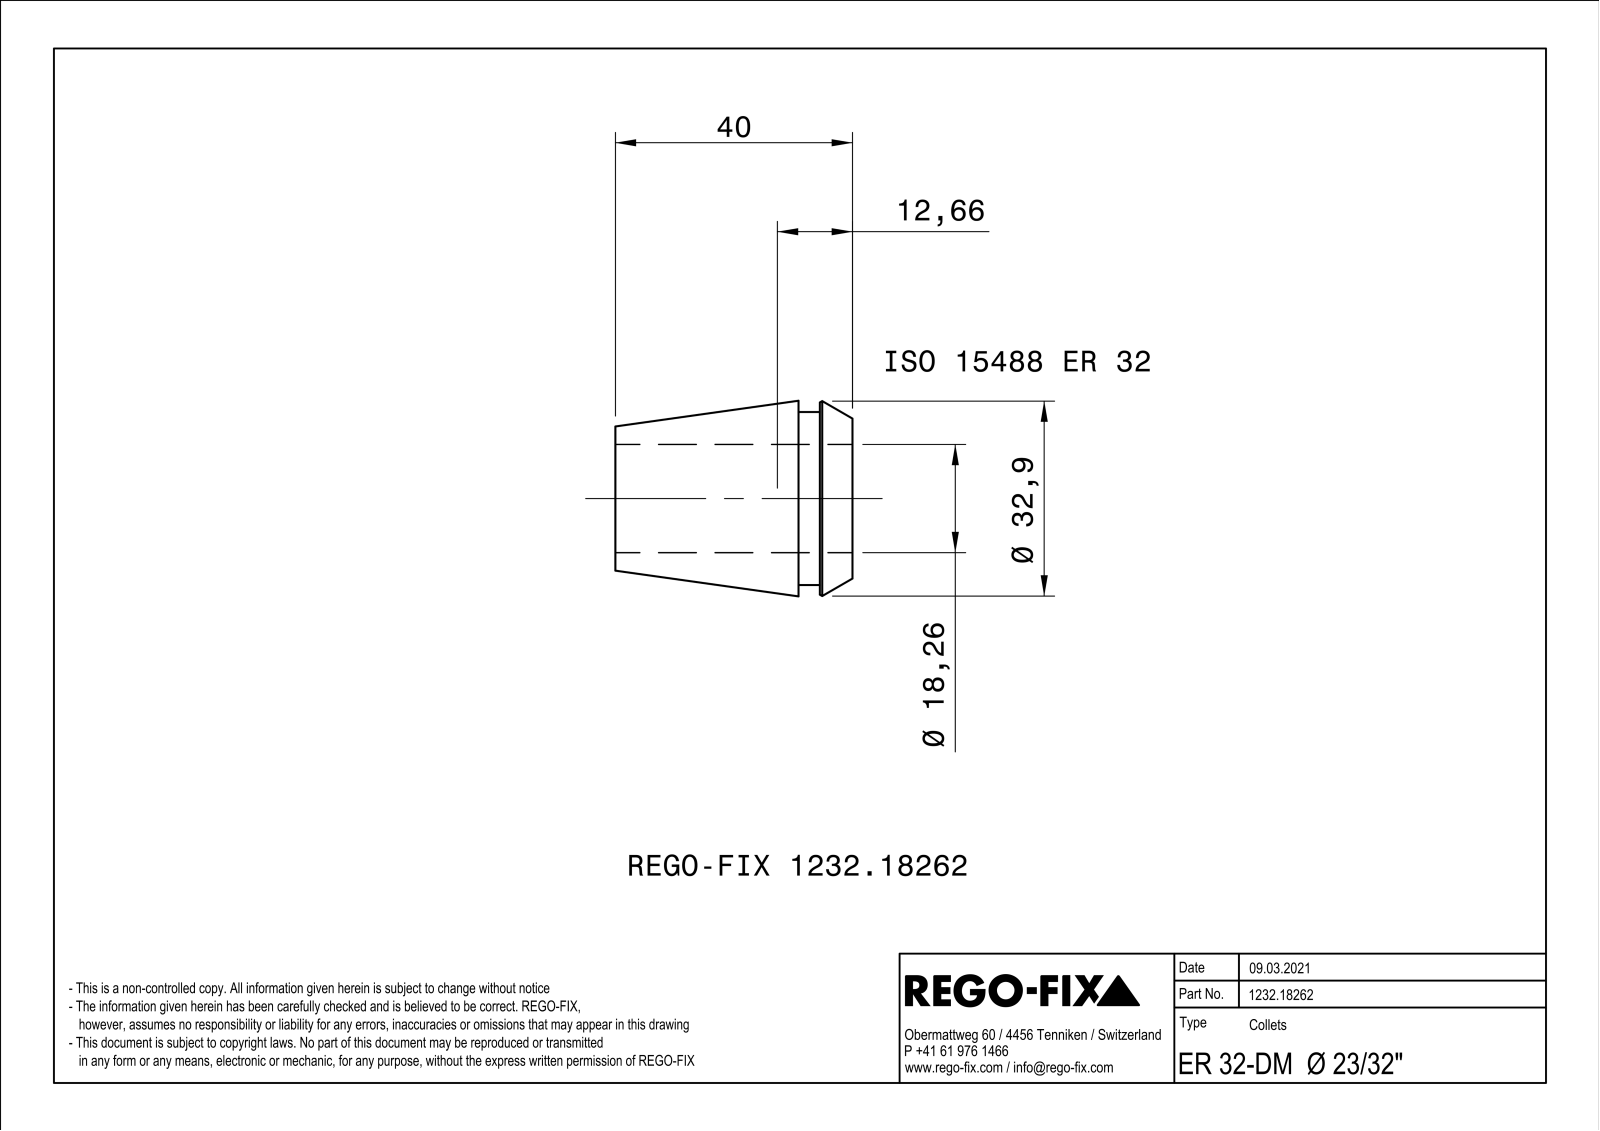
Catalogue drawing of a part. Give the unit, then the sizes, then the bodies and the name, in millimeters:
Units: millimetres
Overall size (bounding box): 40 × 32.98 × 32.98
Round holes (diameter × count): ⌀18.26 ×1
Round bosses / shafts (diameter × count): ⌀29.2 ×1
Main face-to-face distances: 1, 9.1, 40, 30.9, 5.5, 3.6, 34.5, 16, 10.5, 6.9
Volume: 13 484 mm³ · Surface area: 10 852 mm²
Bodies: 1 solid, 154 faces (80 planar, 9 cylindrical, 65 other)
Part name (STEP PRODUCT): NOCUT
STEP written by: SIEMENS PLM Software Solid Edge ST10 (AUTOMOTIVE_DESIGN)
